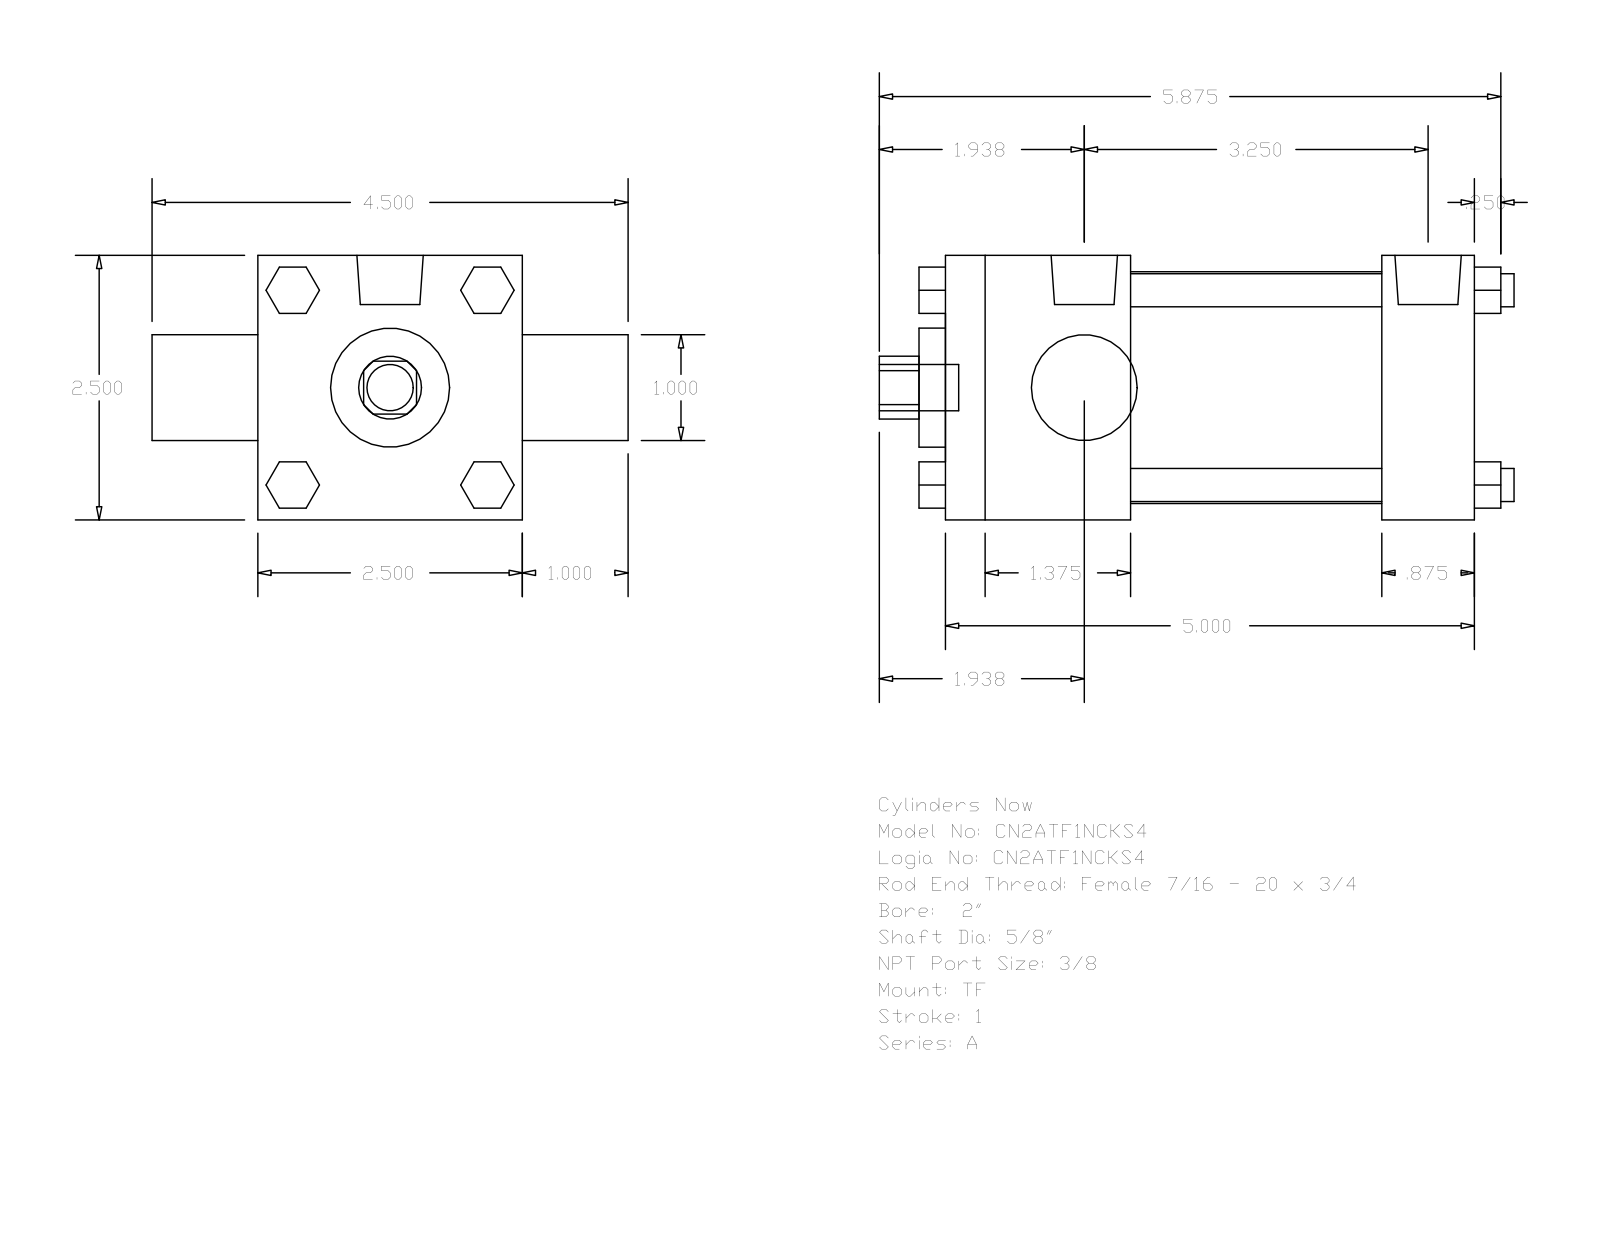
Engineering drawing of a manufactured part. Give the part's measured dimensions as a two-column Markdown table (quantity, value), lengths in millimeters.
| quantity | value |
| --- | --- |
| part name | A_TF__0200_0.625 |
| STEP written by | GSSL Pune (CONFIG_CONTROL_DESIGN) |
| units | millimeters |
| bodies | 0 solids, 120 faces (92 planar, 28 cylindrical, 0 other) |
| overall size | 152.4 × 114.3 × 63.5 |
| round holes (diameter × count) | 15.88 × 1, 25.4 × 1, 28.57 × 1, 55.63 × 1 |
| round bosses / shafts (diameter × count) | 7.94 × 4, 5.56 × 3, 15.93 × 2, 11.11 × 1 |
| partial cylindrical surfaces (radius × count) | 7.54 × 1 |
| main face-to-face distances | 63.5, 127, 44.45, 104.77, 60.32, 82.55, 22.23, 25.4, 88.9, 50.8 |
